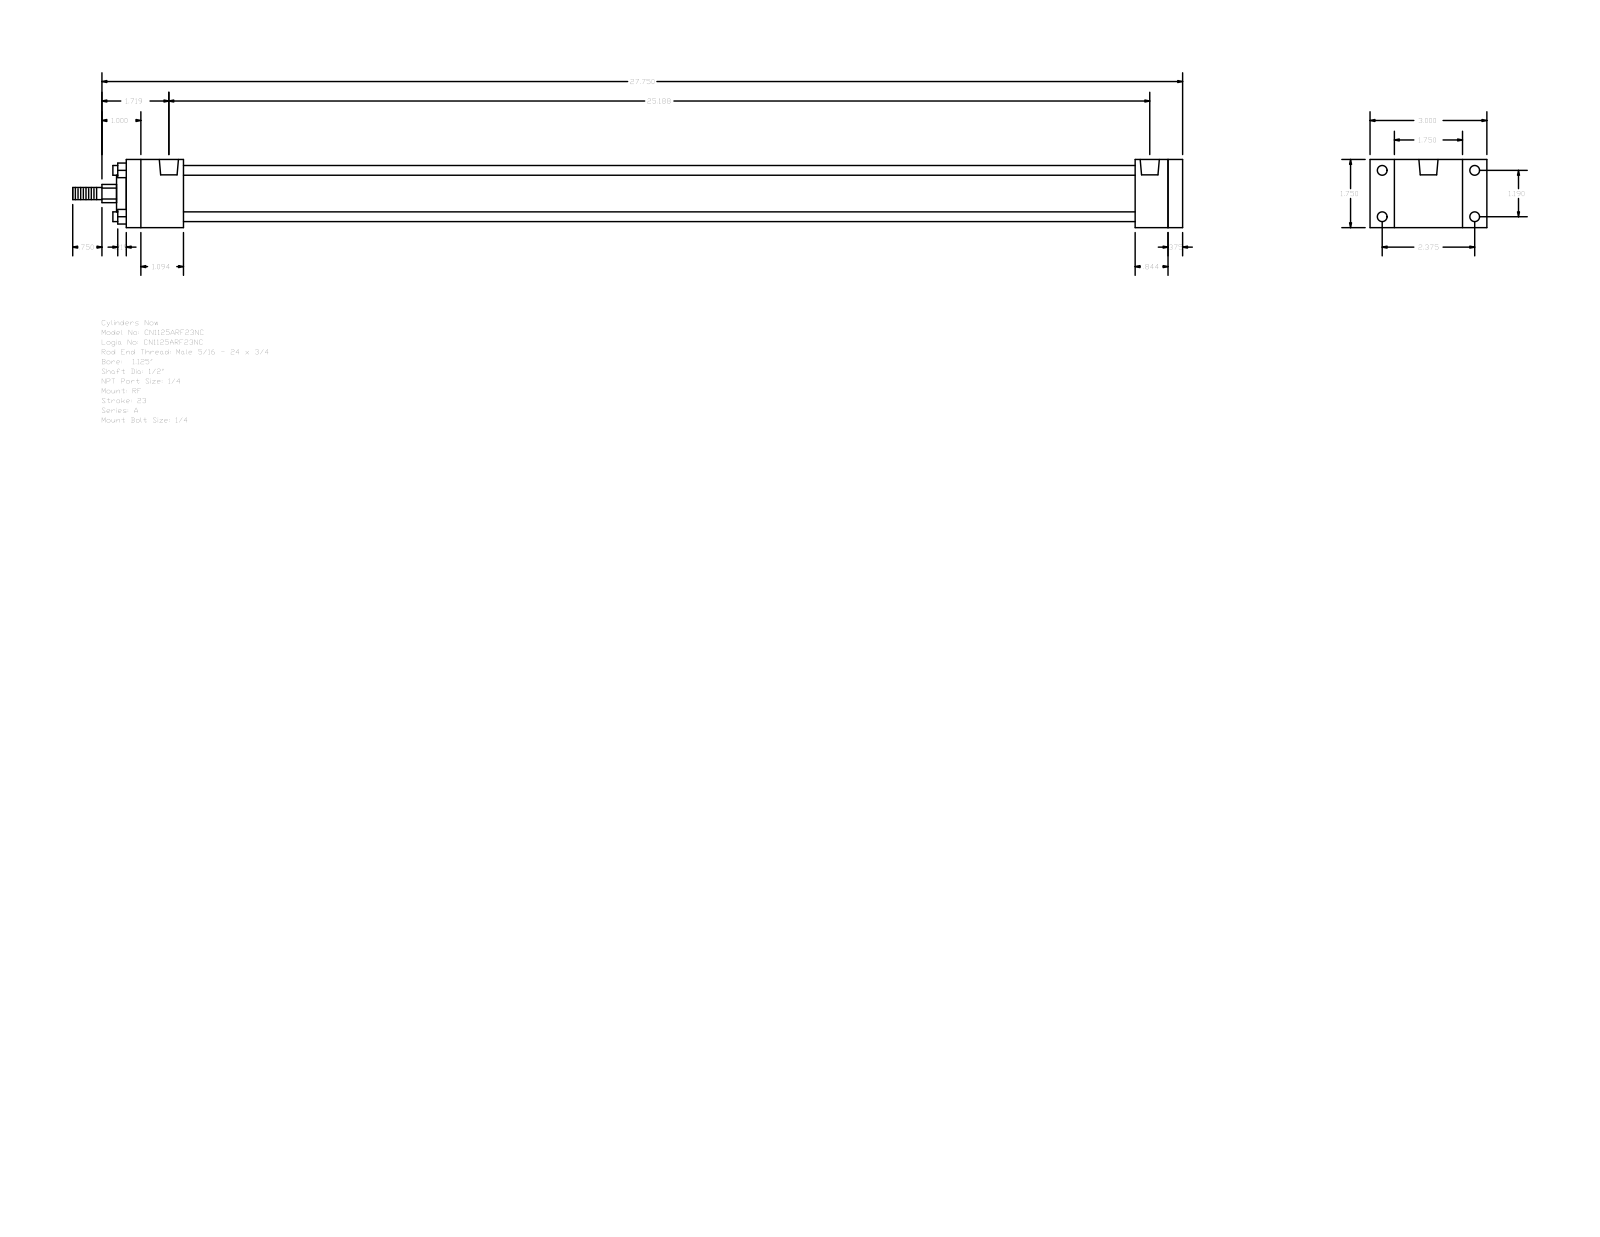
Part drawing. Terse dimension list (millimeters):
name: A_RF__0112_0.5
written by: GSSL Pune (CONFIG_CONTROL_DESIGN)
unit: mm
bodies: 0 solids, 92 faces (64 planar, 28 cylindrical, 0 other)
size: 723.9 × 76.2 × 44.45
holes: 4× ⌀5.56, 4× ⌀6.35, 2× ⌀12.49
bosses: 4× ⌀6.35, 1× ⌀31.88, 1× ⌀23.81, 1× ⌀12.7, 1× ⌀7.94
rounds: 1× R5.94
face distances: 44.46, 9.52, 679.45, 688.97, 37.3, 658.01, 620.71, 642.15, 651.67, 21.44
hole spacings: 30.22, 60.32, 67.47, 636.59, 1.58, 1.59, 638.17, 638.18
